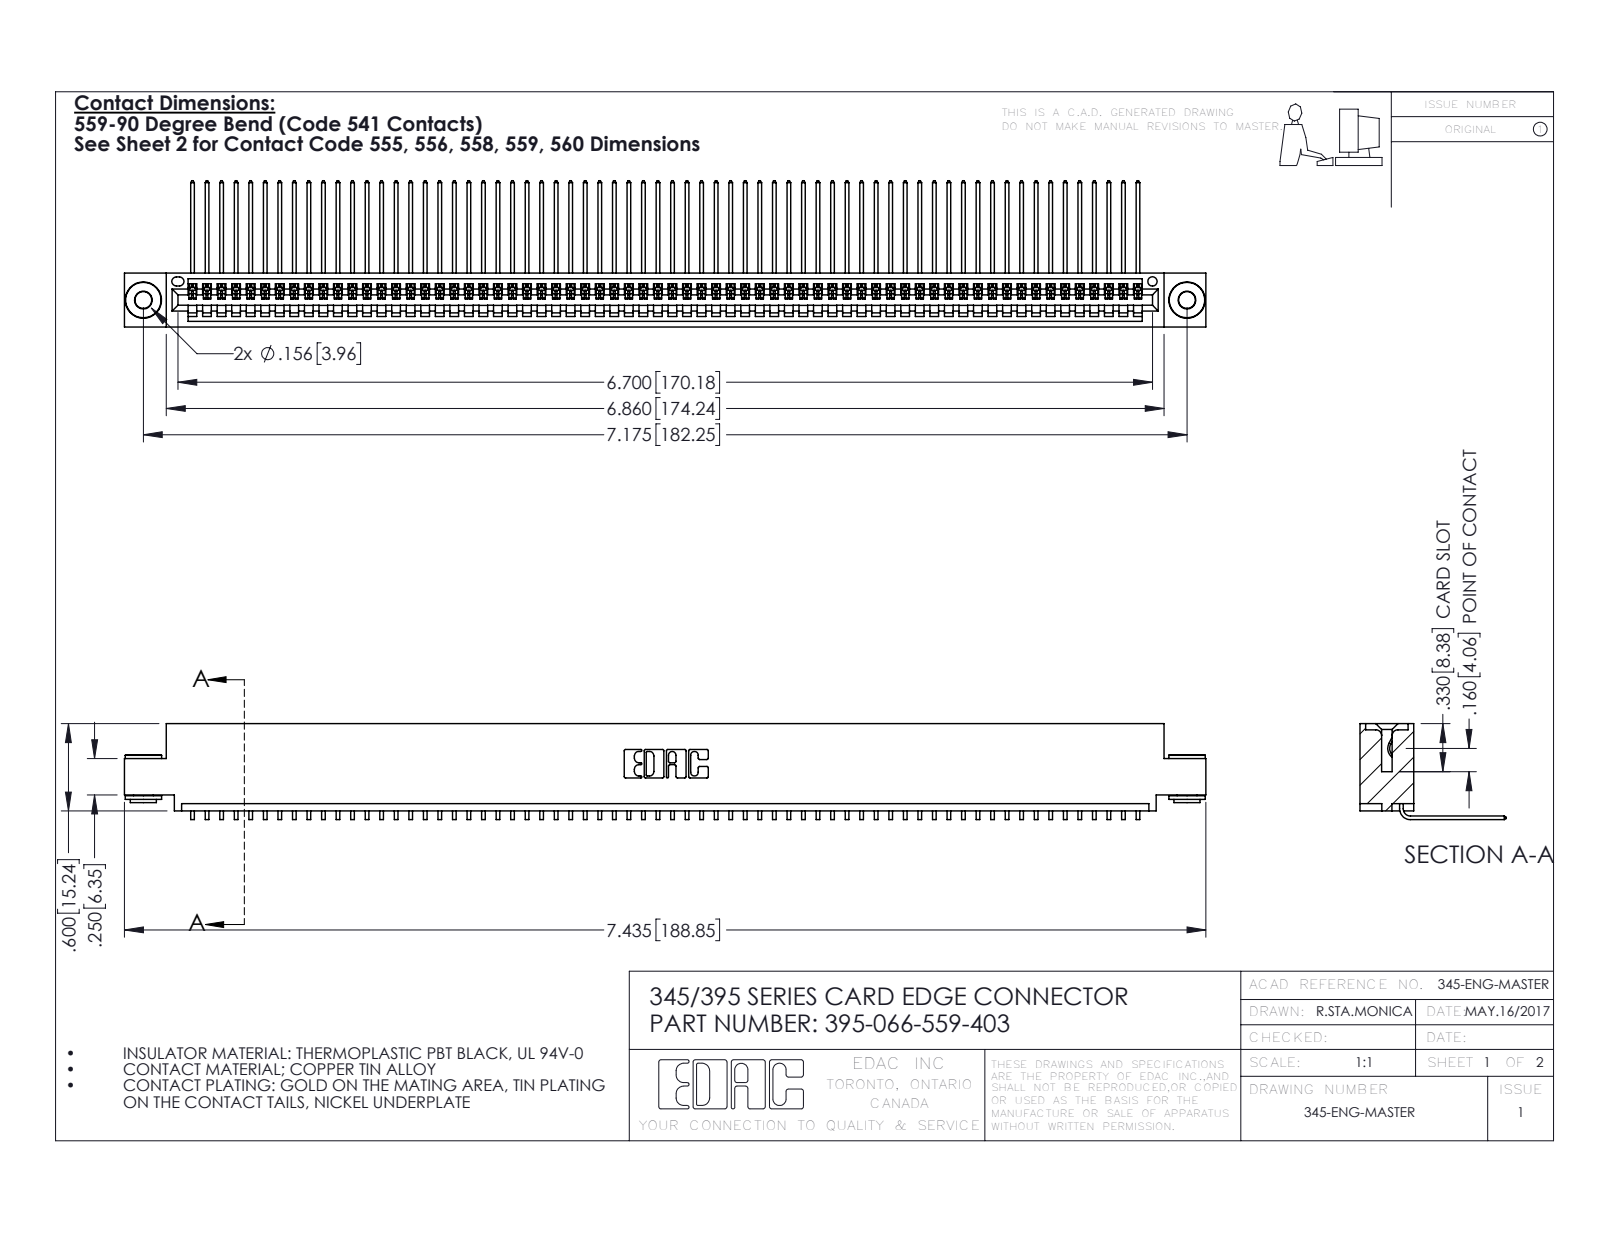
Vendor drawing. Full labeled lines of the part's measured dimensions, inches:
Part name (STEP PRODUCT): 345 Part_0.110 Offset - 0.156 Dia-TH; 345-250-002_345-250-002-102; 395-066-559-403; 345-292-001_558 559 Tail - 1
STEP written by: SolidWorks 2016 (CONFIG_CONTROL_DESIGN)
Units: inches
Bodies: 69 solids, 4128 faces (2866 planar, 1254 cylindrical, 8 other)
Overall size (bounding box): 7.435 × 1.005 × 0.659
Volume: 1.117 in³ · Surface area: 40.66 in²
Round holes (diameter × count): ⌀0.116 ×2, ⌀0.156 ×2, ⌀0.064 ×1
Round bosses / shafts (diameter × count): ⌀0.25 ×2, ⌀0.18 ×2, ⌀0.136 ×2
Partial cylindrical surfaces — rounded edges, fillets, slot ends (radius × count): R0.006 ×132, R0.01 ×22, R0.007 ×6, R0.031 ×6, R0.026 ×3, R0.031 ×2, R0.04 ×2, R0.014 ×1
Main face-to-face distances: 0.072, 0.298, 0.37, 0.2, 0.025, 0.098, 0.272, 0.225, 0.149, 0.072
Hole centre spacings: 0.27, 6.939, 7.175
